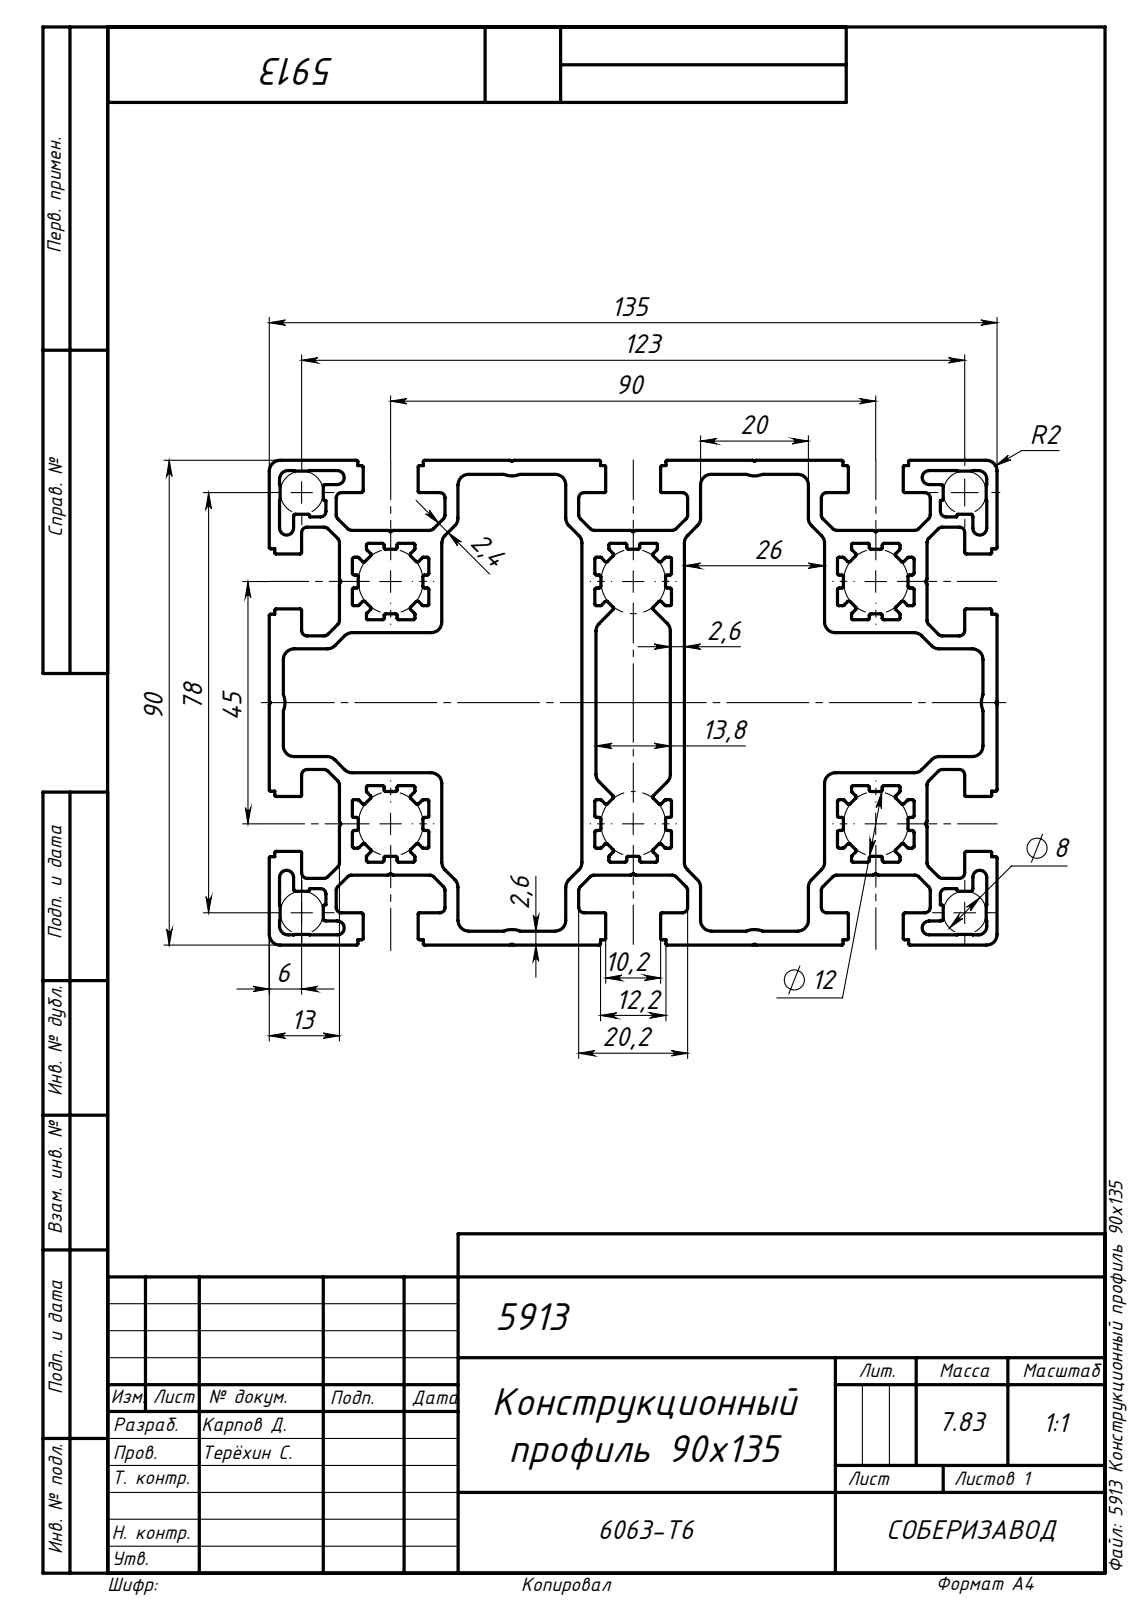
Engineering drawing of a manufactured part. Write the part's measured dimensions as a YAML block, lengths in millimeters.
part_name: "5913 Конструкционный профиль 90х135"
step_written_by: "SolidWorks 2018 (AUTOMOTIVE_DESIGN)"
units: millimeters
bodies: {solids: 1, faces: 1048, planar: 554, cylindrical: 494, other: 0}
overall_size: [1000, 135, 90]
volume: 2899000
surface_area: 2037000
partial_cylinders:
  - {radius: 0.3, count: 184}
  - {radius: 0.25, count: 132}
  - {radius: 1, count: 64}
  - {radius: 2, count: 48}
  - {radius: 0.4, count: 24}
  - {radius: 0.35, count: 8}
  - {radius: 1.3, count: 8}
  - {radius: 4, count: 6}
face_to_face_distances: [45, 58, 77, 19, 26, 90, 2.6, 13, 74.4, 32]
